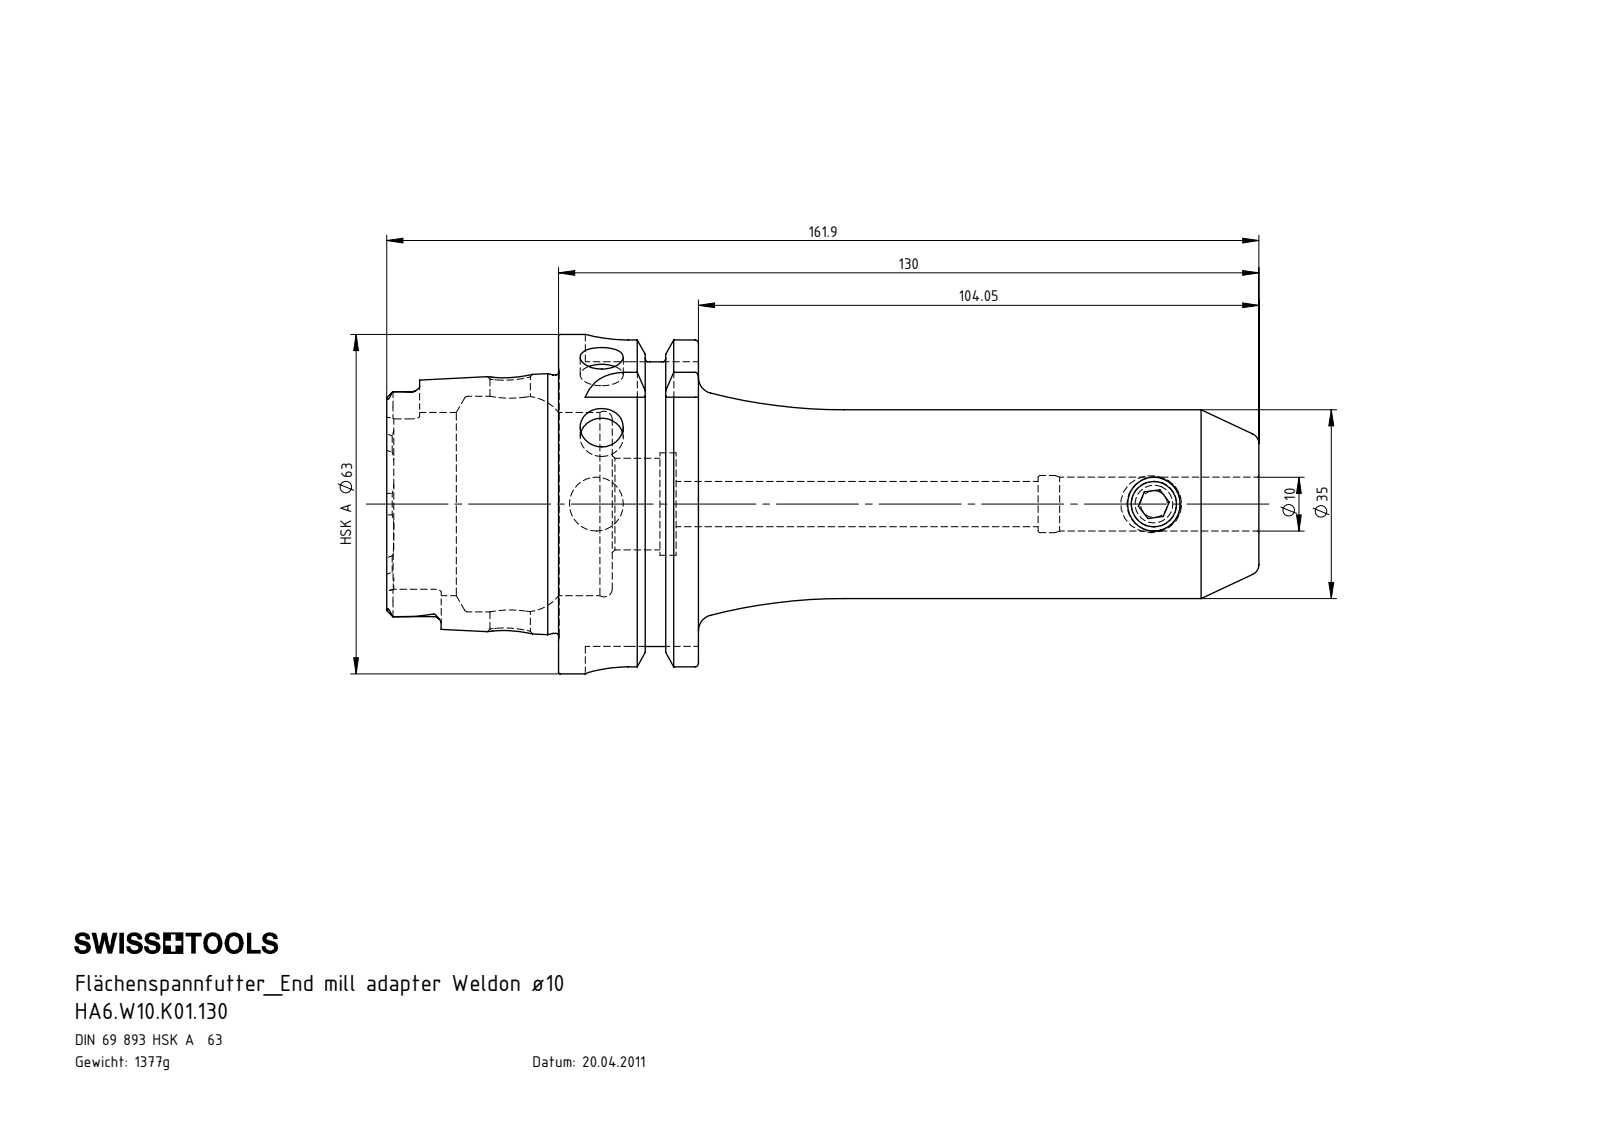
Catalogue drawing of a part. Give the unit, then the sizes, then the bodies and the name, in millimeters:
Units: millimetres
Overall size (bounding box): 161.9 × 63 × 63
Round holes (diameter × count): ⌀8 ×2, ⌀10 ×2, ⌀7.5 ×1, ⌀8.4 ×1, ⌀8.5 ×1, ⌀10.6 ×1, ⌀17 ×1, ⌀19 ×1, ⌀34 ×1, ⌀40 ×1
Round bosses / shafts (diameter × count): ⌀63 ×1, ⌀54.95 ×1, ⌀47.94 ×1, ⌀35 ×1, ⌀10 ×1
Partial cylindrical surfaces — rounded edges, fillets, slot ends (radius × count): R1.4 ×6, R2.88 ×4, R8 ×4
Main face-to-face distances: 25.95, 16, 9.95, 31.9, 41.85, 57.85, 161.9, 130, 120.05, 104.05
Hole centre spacings: 103.5
Volume: 175 372 mm³ · Surface area: 36 839 mm²
Bodies: 2 solids, 210 faces (58 planar, 57 cylindrical, 95 other)
Part name (STEP PRODUCT): HA6-W10.K01.130_A_Fertigbearbeitung; HA6-W10.K01.130; W10-ER1.001.012
STEP written by: SolidWorks 2012 (CONFIG_CONTROL_DESIGN)
